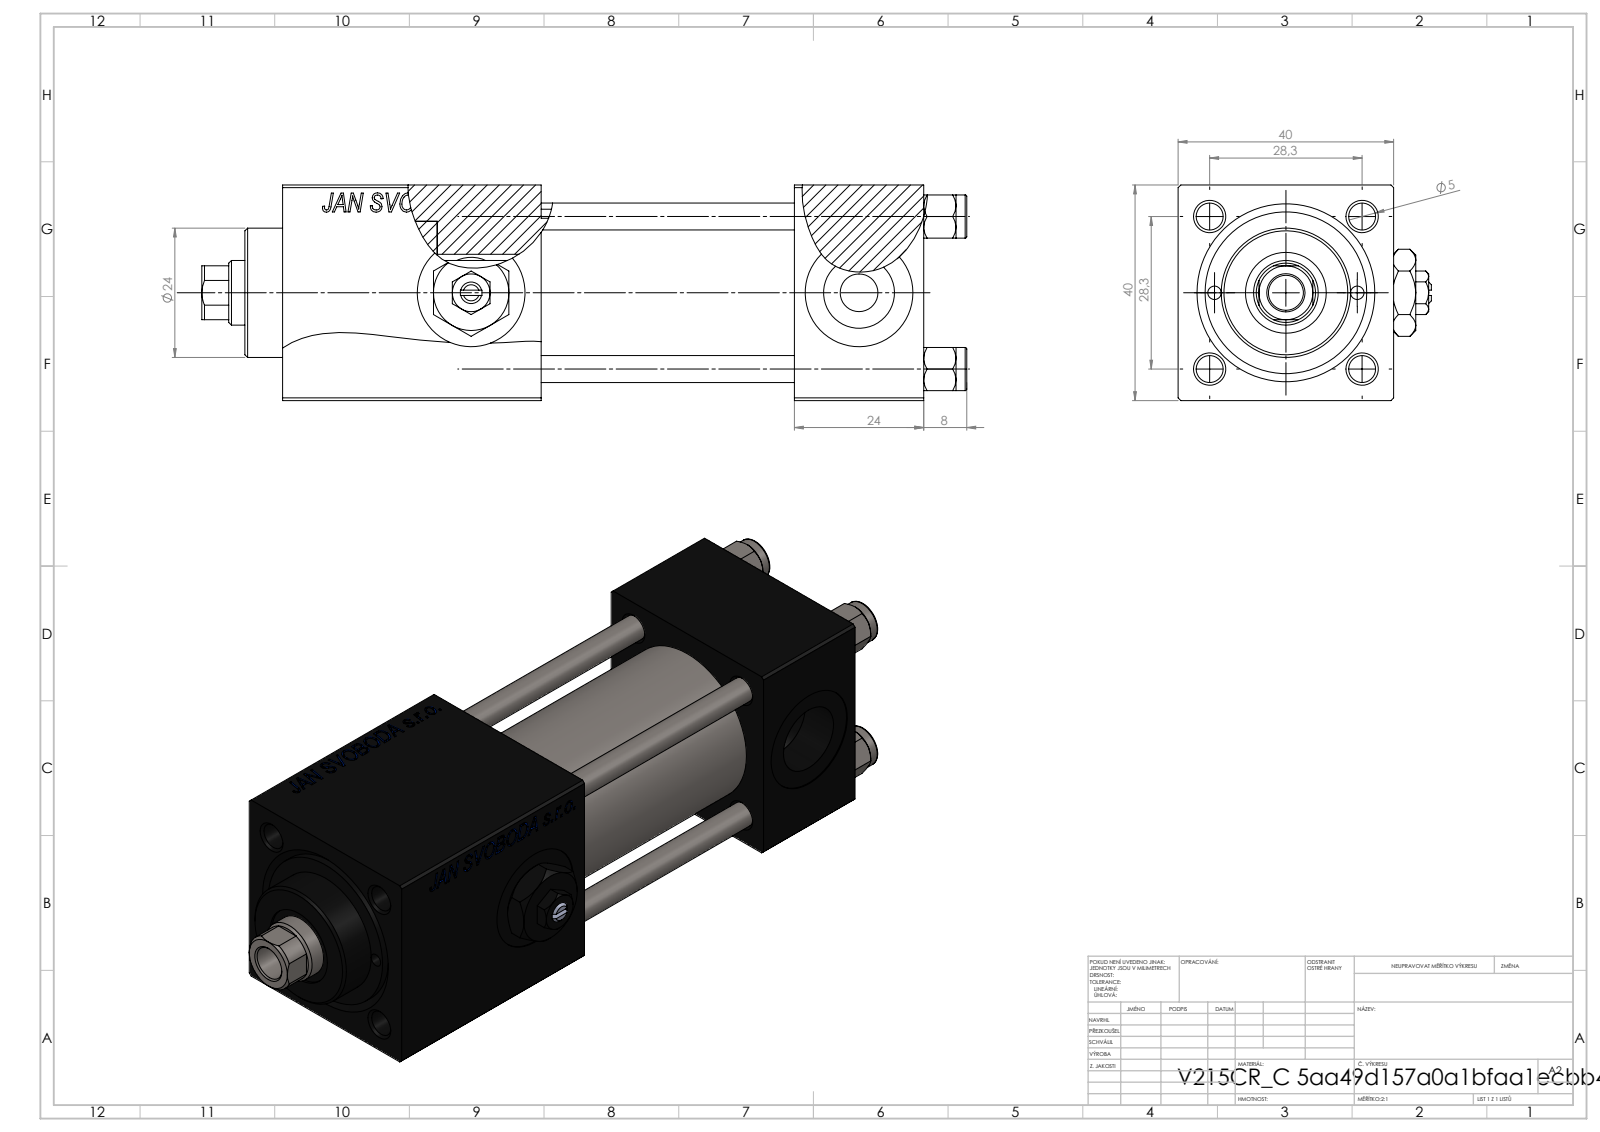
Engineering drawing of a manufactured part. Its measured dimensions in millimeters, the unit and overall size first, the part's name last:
Units: millimetres
Overall size (bounding box): 142 × 47 × 40
Round holes (diameter × count): ⌀5 ×4, ⌀20 ×3, ⌀2.5 ×2, ⌀7 ×2, ⌀13.16 ×2, ⌀6.5 ×1, ⌀12 ×1, ⌀15 ×1, ⌀25 ×1, ⌀30 ×1
Round bosses / shafts (diameter × count): ⌀8 ×4, ⌀31 ×1, ⌀24 ×1
Partial cylindrical surfaces — rounded edges, fillets, slot ends (radius × count): R5.5 ×1
Main face-to-face distances: 40, 24, 90.3, 66.3, 48, 47, 71, 19.3, 119, 95
Hole centre spacings: 14.18, 20.01, 28.3, 30.84, 13.25, 40.02, 26.5, 72
Volume: 141 941 mm³ · Surface area: 55 199 mm²
Bodies: 12 solids, 1201 faces (551 planar, 94 cylindrical, 556 other)
Part name (STEP PRODUCT): V215CR_C_Body; Zatka_pro_OIL_PORT; V215_VC_A; V215CR_VCP_C (+2 more)
STEP written by: SolidWorks 2019 (CONFIG_CONTROL_DESIGN)
